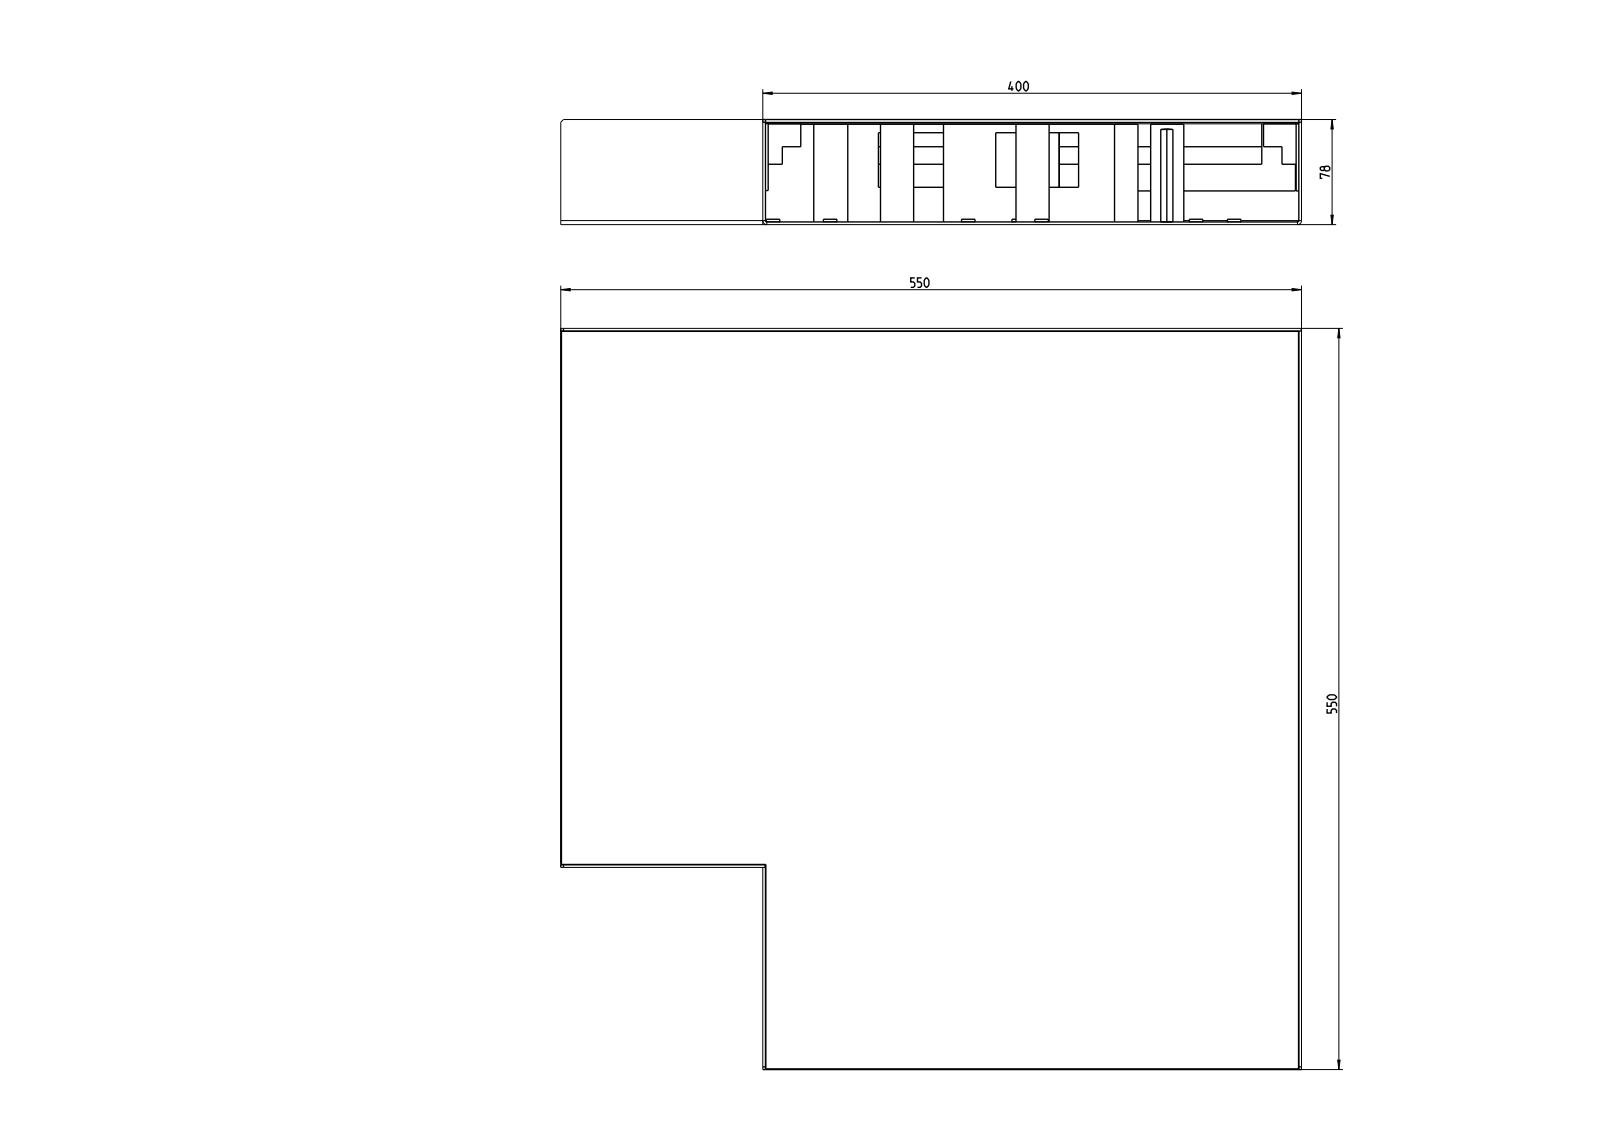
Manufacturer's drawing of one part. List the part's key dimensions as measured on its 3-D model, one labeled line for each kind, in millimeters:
Part name (STEP PRODUCT): T-01227; T-01220; T-01248; T-01247 (+8 more)
STEP written by: CREO PARAMETRIC BY PTC INC, 2022024 (AUTOMOTIVE_DESIGN)
Units: millimetres
Bodies: 18 solids, 498 faces (341 planar, 105 cylindrical, 52 other)
Overall size (bounding box): 713.76 × 655.09 × 78.23
Volume: 3 997 000 mm³ · Surface area: 2 057 000 mm²
Round holes (diameter × count): ⌀6 ×12, ⌀6.5 ×8, ⌀13.6 ×7
Round bosses / shafts (diameter × count): ⌀10 ×12
Partial cylindrical surfaces — rounded edges, fillets, slot ends (radius × count): R0.1 ×4, R1 ×4, R3 ×4
Main face-to-face distances: 2, 72.8, 1, 73.8, 74.8, 75.8, 4, 396, 24.6, 7.8
Hole centre spacings: 20, 300, 315.47, 97.57, 300.67, 212.6, 33, 53
